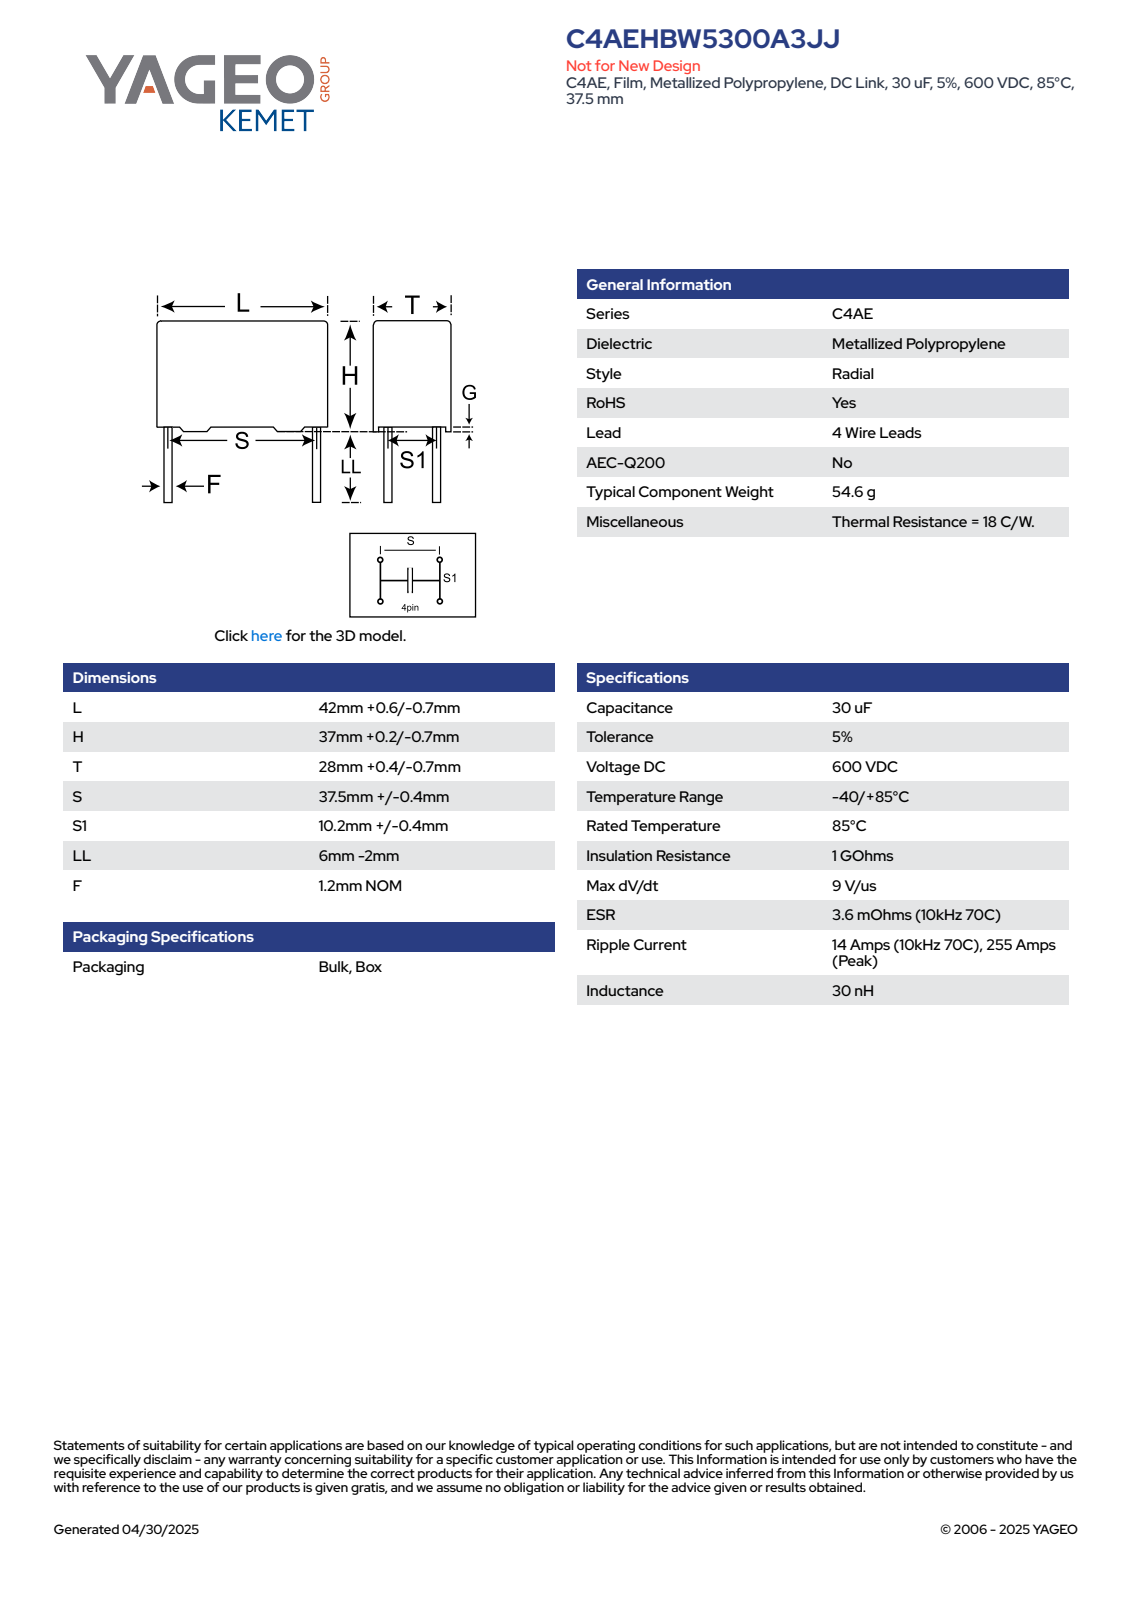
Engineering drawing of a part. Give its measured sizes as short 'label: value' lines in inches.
name: CFP_RB4G_42X37X28_L42.6H37.2T28.4S37.5S110.2LL4F1.2G0.5
written by: SolidWorks 2014 (AUTOMOTIVE_DESIGN)
unit: in
bodies: 4 solids, 91 faces (83 planar, 8 cylindrical, 0 other)
size: 1.677 × 1.622 × 1.119
volume: 2.712 in³; area: 12.11 in²
bosses: 4× ⌀0.047
face distances: 1.118, 1.445, 1.677, 0.02, 1.465, 0.079, 1.039, 0.961, 0.663, 0.157
